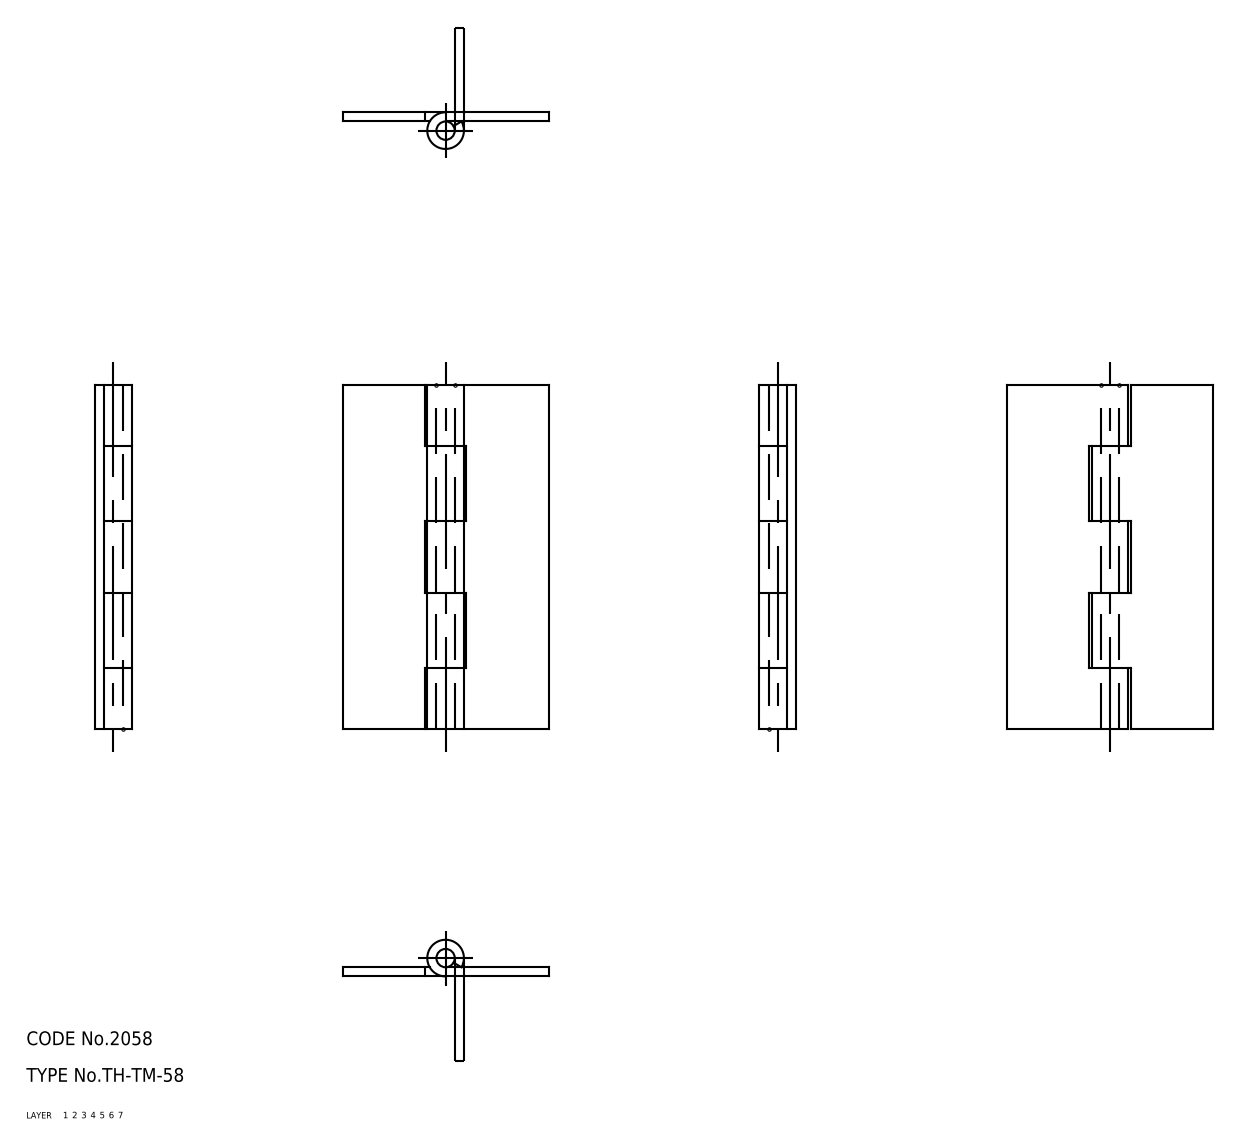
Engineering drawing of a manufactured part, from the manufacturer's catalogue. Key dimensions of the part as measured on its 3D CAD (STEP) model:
Part name (STEP PRODUCT): hinge piece_B; hinge piece_A; shaft; TH_TM_58_24315_36
STEP written by: CADfix (AUTOMOTIVE_DESIGN)
Units: millimetres
Bodies: 3 solids, 42 faces (0 planar, 0 cylindrical, 42 other)
Overall size (bounding box): 75 × 45 × 8
Volume: 9 369 mm³ · Surface area: 10 541 mm²
